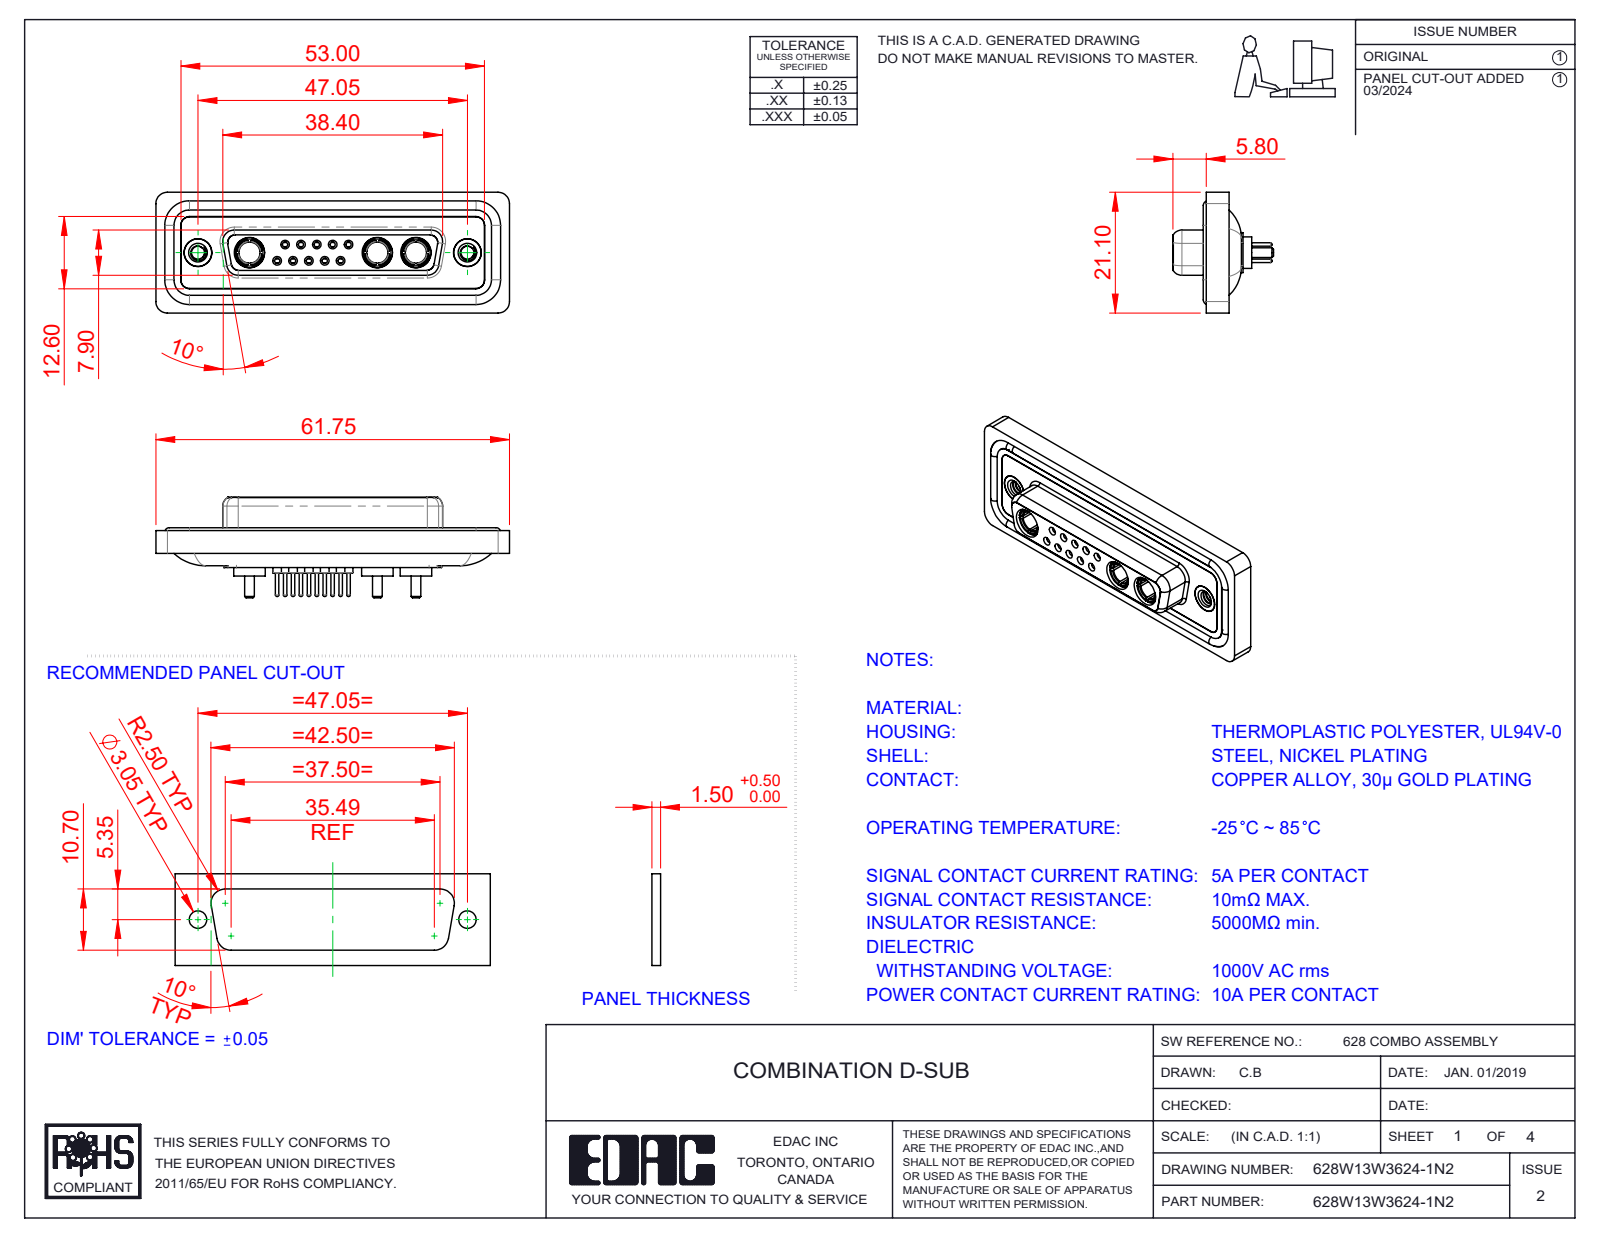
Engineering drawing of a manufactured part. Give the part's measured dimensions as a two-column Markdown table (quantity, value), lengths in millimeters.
| quantity | value |
| --- | --- |
| part name | 628Combo Contact Row 2_24; 628Combo Waterproof Housing_25 Contacts; 628Combo Shell Front_25 Contacts; 628Combo Housing_13W3 (+5 more) |
| STEP written by | SolidWorks 2023 (CONFIG_CONTROL_DESIGN) |
| units | millimeters |
| bodies | 23 solids, 1158 faces (342 planar, 447 cylindrical, 369 other) |
| overall size | 61.75 × 21.1 × 17.55 |
| volume | 8 229 mm³ |
| surface area | 13 671 mm² |
| round holes (diameter × count) | 0.9 × 10, 1.1 × 10, 1.5 × 10, 2 × 10, 1.6 × 5, 1.7 × 5, 4.85 × 5, 3.7 × 3, 5.3 × 3, 2.26 × 2, 4 × 2, 4.05 × 2 |
| round bosses / shafts (diameter × count) | 2.2 × 10, 0.6 × 10, 1.6 × 9, 5.5 × 3, 5.2 × 3, 4.96 × 3, 4.75 × 3, 3.75 × 3 |
| partial cylindrical surfaces (radius × count) | 1.5 × 22, 2 × 18, 1.35 × 8, 1.6 × 8, 0.25 × 4, 0.5 × 4, 0.6 × 4, 0.65 × 4 |
| main face-to-face distances | 0.4, 1.8, 7.45, 5.65, 0.5, 6.6, 7.05, 1.6, 2.9, 1.1 |
| hole center spacings | 3.16, 2.77, 5.03, 5.04, 5.54, 8.31, 7.49, 2.76 |
